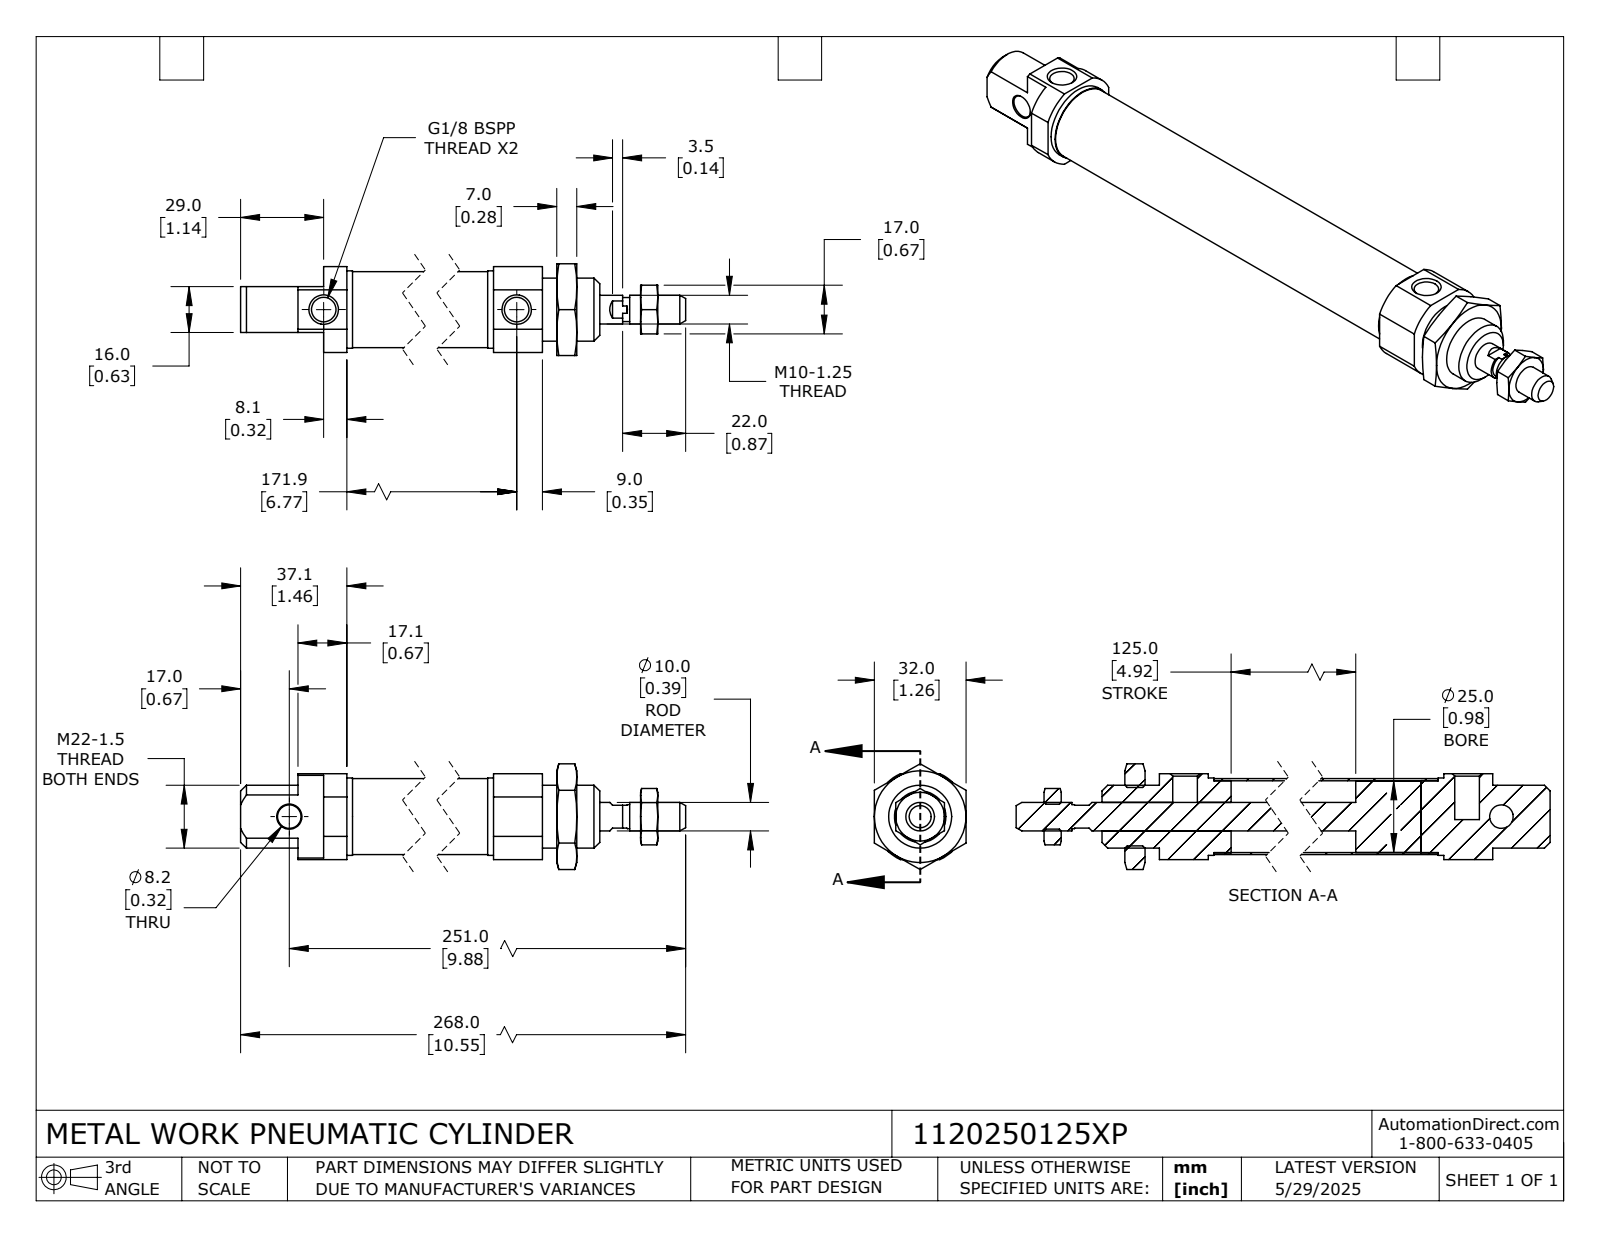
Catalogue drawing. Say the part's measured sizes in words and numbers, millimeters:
The part is named "1120250125XP; 1120250125XP_BODY; 1120250125XP_ROD". Its 3-D file was written by "SolidWorks 2024 (CONFIG_CONTROL_DESIGN)". It is 6 solids with 144 faces: 54 planar, 44 cylindrical and 46 other. Overall it measures 268 by 36.95 by 32 millimeters. Its volume is 82 122 cubic millimeters and its surface area 50 716 square millimeters. Round holes: 2 of diameter 8.57, 1 of diameter 8.2, 1 of diameter 8.65, 1 of diameter 20.38, 1 of diameter 25. Round bosses or shafts: 1 of diameter 27, 1 of diameter 26.52, 1 of diameter 25.15, 1 of diameter 22, 1 of diameter 10, 1 of diameter 8.4. Partial cylindrical surfaces (rounded edges, fillets, slot ends): 1 of radius 16.5. The main face-to-face distances are 7, 8, 37.1, 23, 30, 192.9, 172.9, 25.1, 16, 155.8. The hole center spacings are 180.
